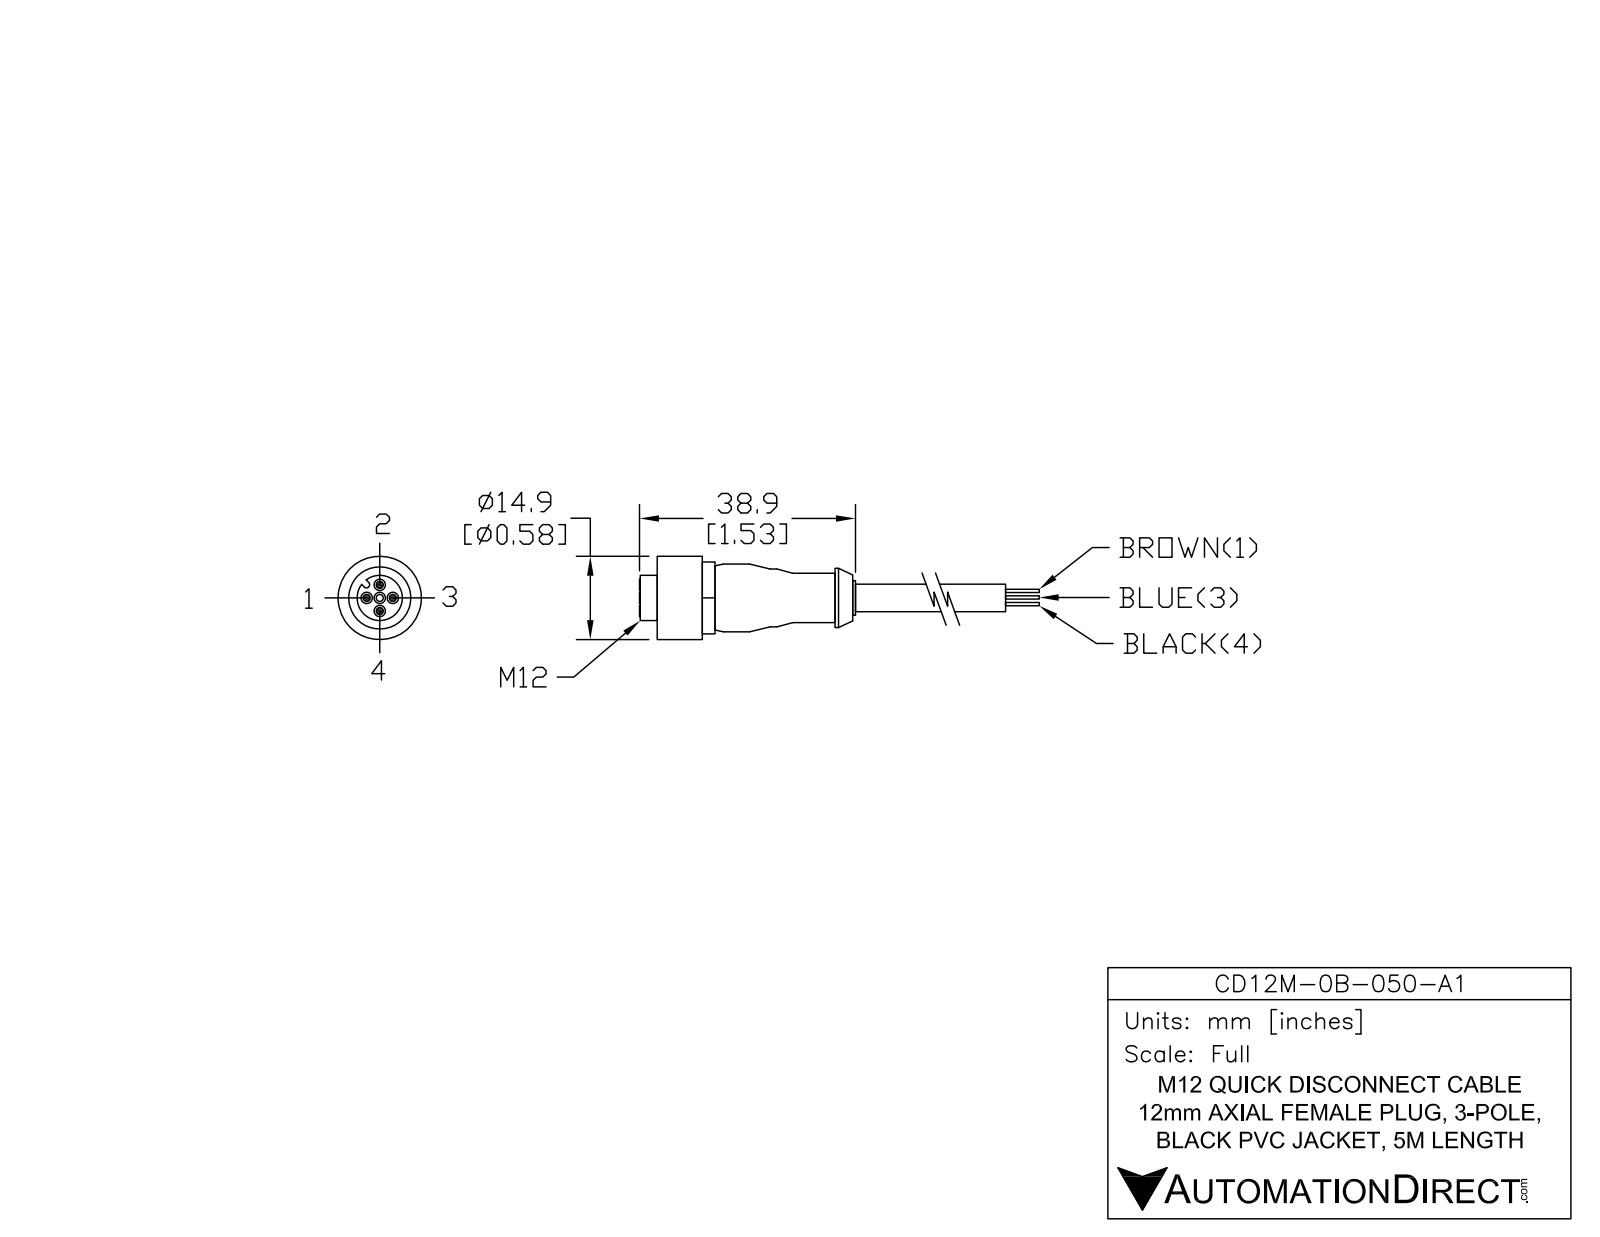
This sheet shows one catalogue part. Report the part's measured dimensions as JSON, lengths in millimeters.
{"part_name": "CD12M-0B-050-A1", "step_written_by": "SolidWorks 2017 (AUTOMOTIVE_DESIGN)", "units": "millimeters", "bodies": {"solids": 4, "faces": 308, "planar": 195, "cylindrical": 107, "other": 6}, "overall_size": [138.9, 15, 15], "volume_mm3": 5509, "surface_area_mm2": 4482, "round_holes": [[1, 5], [8.5, 1], [12, 1]], "round_bosses_or_shafts": [[12.2, 1], [10.7, 1], [10.4, 1], [8.9, 1], [8.1, 1], [4.9, 1]], "partial_cylinders_radius": [[0.55, 1], [7.5, 1]], "face_to_face_distances": [25.3, 1.4, 1.7, 8.2, 26.7, 37.2, 11.9, 10.5, 6.5, 30.7], "hole_center_spacings": [2.35, 3.32, 4.7]}
